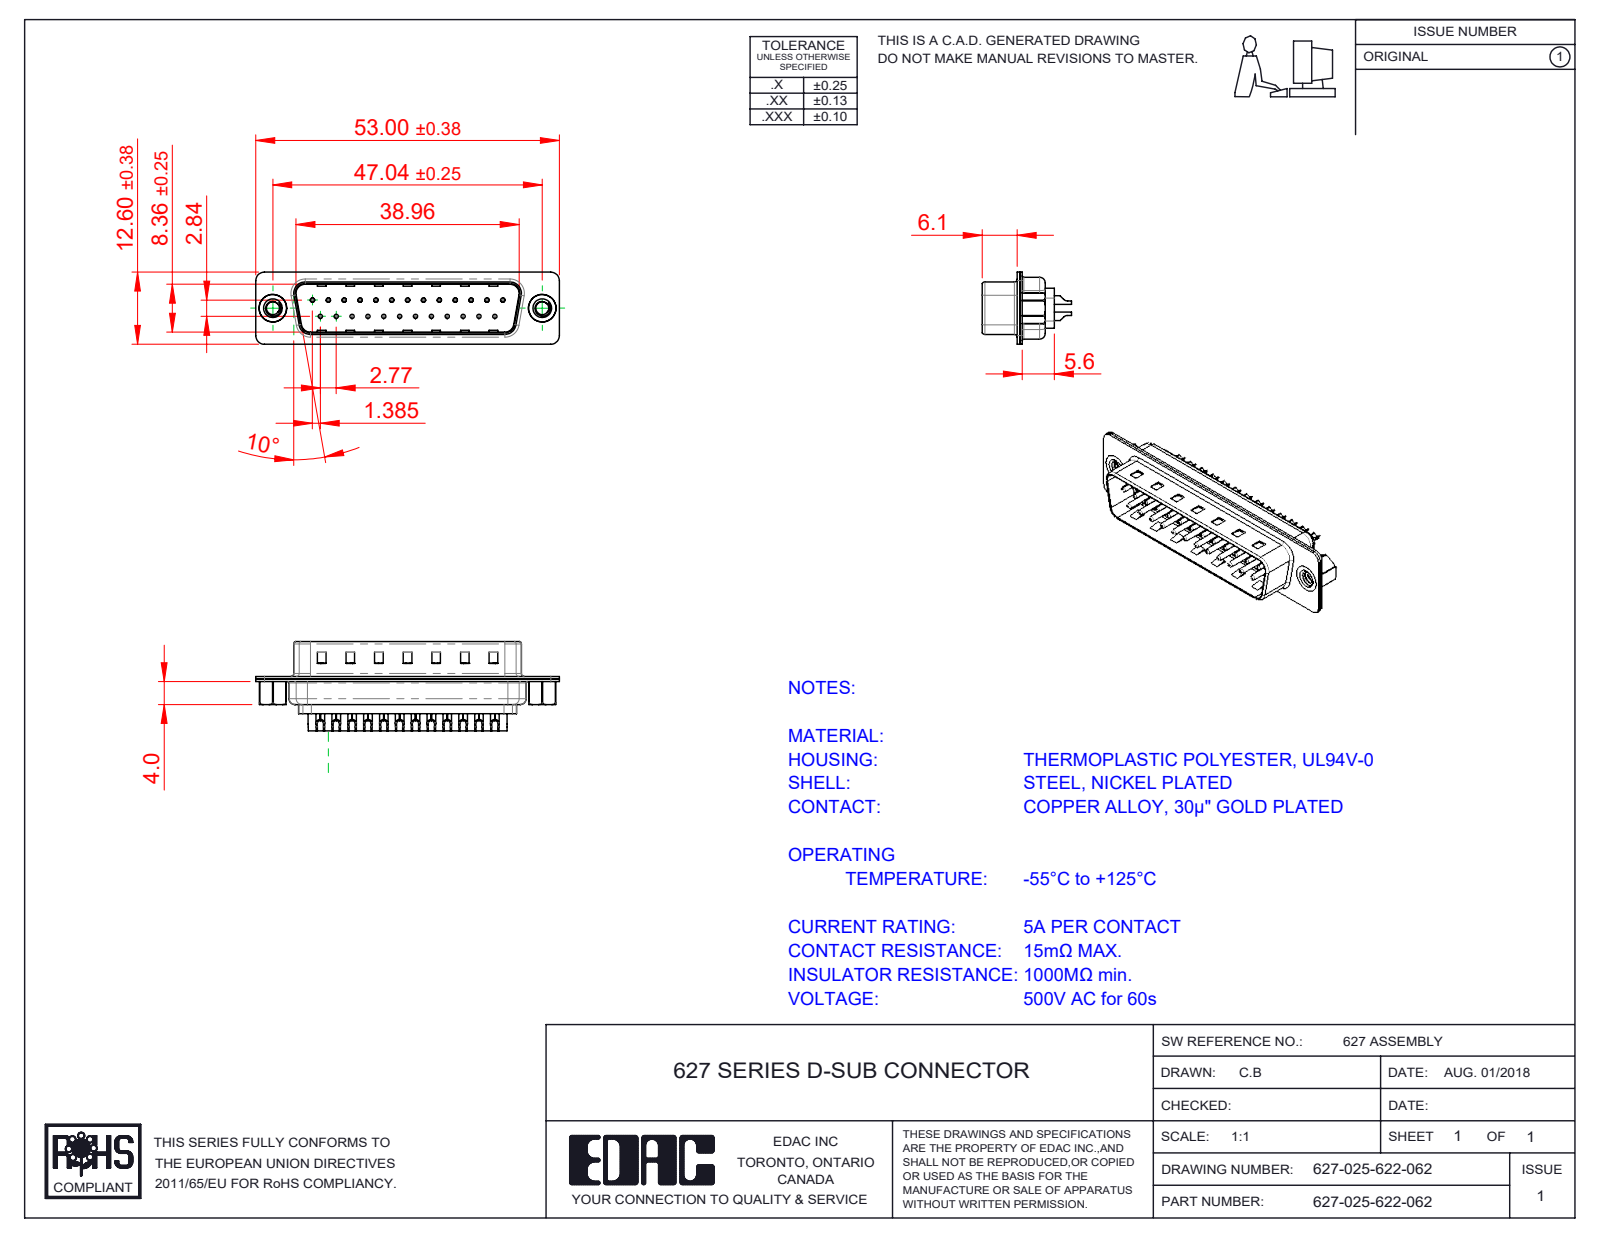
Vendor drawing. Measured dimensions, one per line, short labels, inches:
name: 627 Housing_25 LP; 627-025-622-062; 627 Shell Rear_25 Contacts; 627 Contact Row 1_22L (+3 more)
written by: SolidWorks 2020 (CONFIG_CONTROL_DESIGN)
unit: in
bodies: 30 solids, 1972 faces (521 planar, 860 cylindrical, 591 other)
size: 2.087 × 0.604 × 0.496
volume: 0.164 in³; area: 12.16 in²
holes: 25× ⌀0.014, 25× ⌀0.043, 25× ⌀0.063, 2× ⌀0.089, 2× ⌀0.157, 2× ⌀0.189
bosses: 25× ⌀0.079, 25× ⌀0.059, 25× ⌀0.03, 2× ⌀0.197, 2× ⌀0.193
rounds: 16× R0.059, 12× R0.079, 8× R0.02, 8× R0.063, 6× R0.039, 4× R0.01, 4× R0.024, 4× R0.026
face distances: 0.016, 0.018, 0.032, 0.377, 0.345, 0.035, 0.059, 0.055, 0.256, 0.238
hole spacings: 0.124, 0.327, 0.109, 0.218, 0.436, 0.654, 0.198, 0.198
